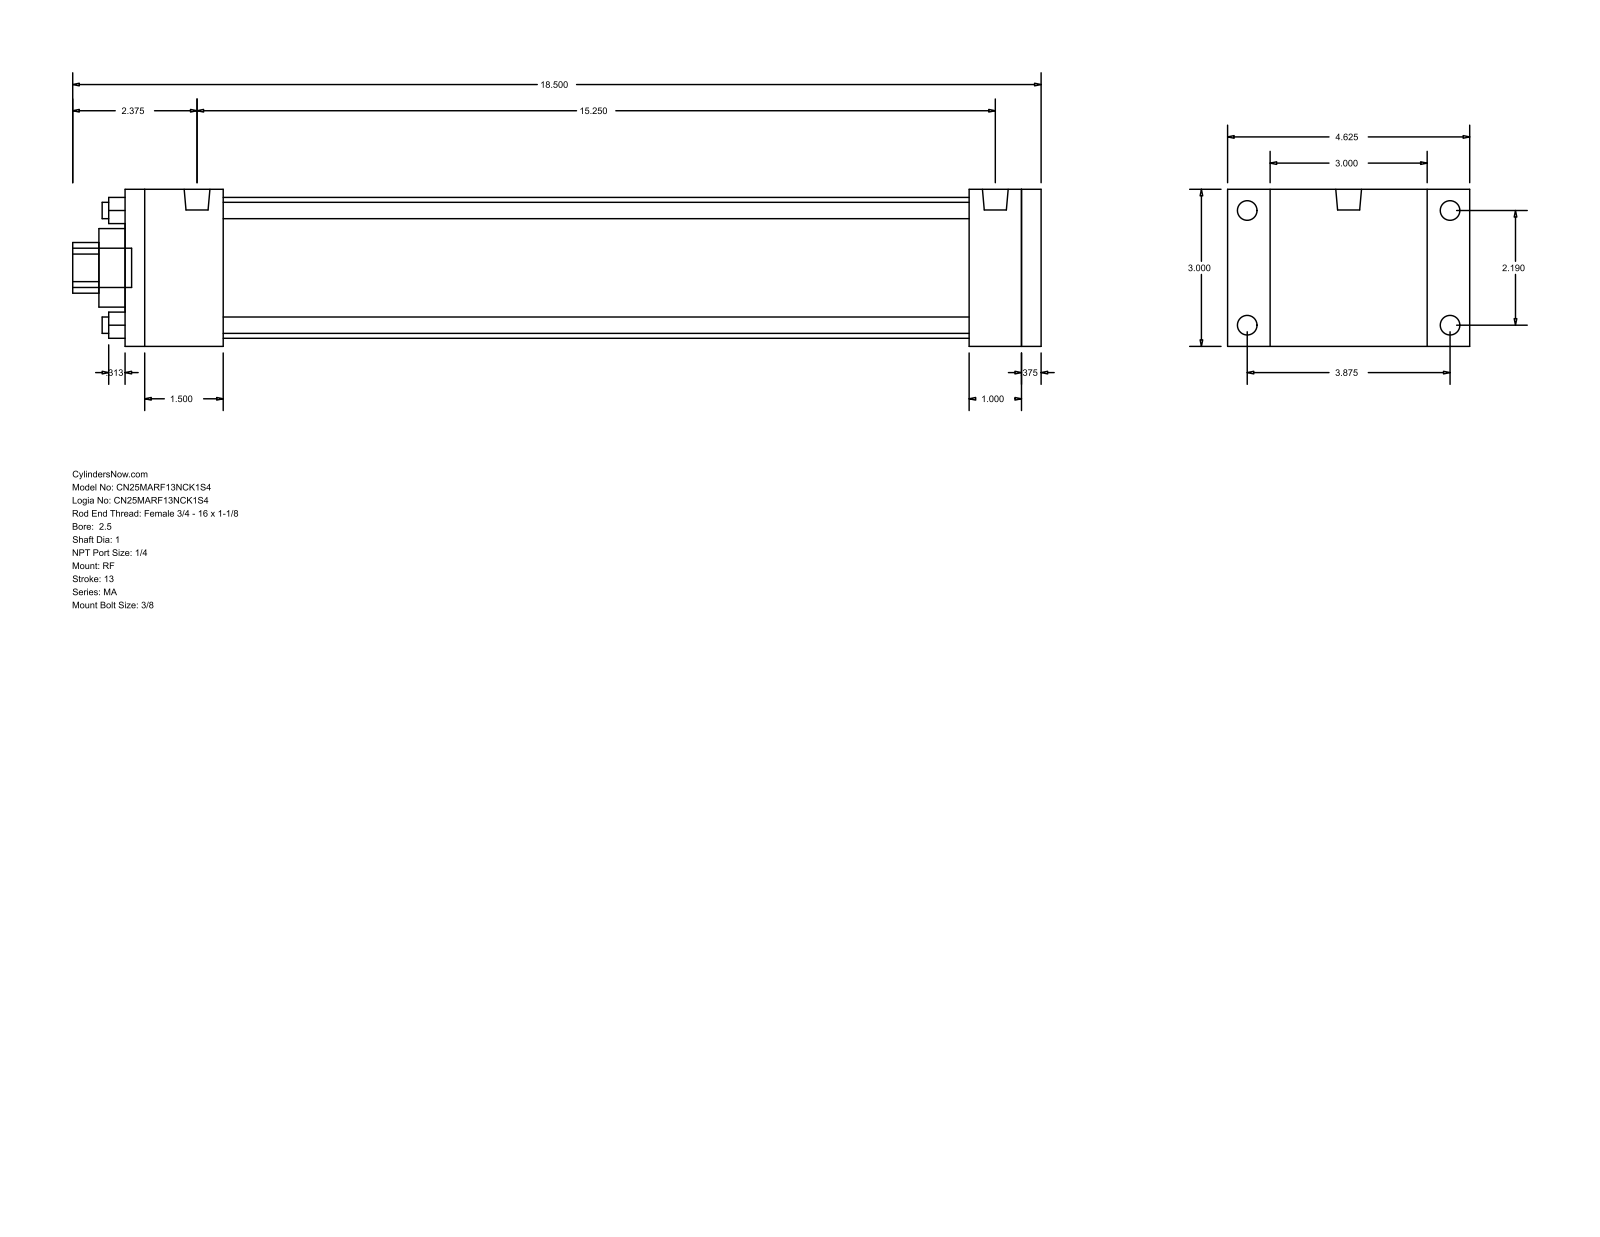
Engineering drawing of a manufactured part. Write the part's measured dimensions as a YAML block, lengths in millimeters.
part_name: "MA_RF__0250_1"
step_written_by: "GSSL Pune (CONFIG_CONTROL_DESIGN)"
units: millimeters
bodies: {solids: 0, faces: 92, planar: 64, cylindrical: 28, other: 0}
overall_size: [469.9, 117.47, 76.2]
round_holes:
  - {diameter: 7.94, count: 4}
  - {diameter: 25.4, count: 1}
  - {diameter: 38.1, count: 1}
  - {diameter: 68.33, count: 1}
round_bosses_or_shafts:
  - {diameter: 9.53, count: 4}
  - {diameter: 7.94, count: 4}
  - {diameter: 12.49, count: 2}
  - {diameter: 19.05, count: 1}
partial_cylinders:
  - {radius: 12.29, count: 1}
face_to_face_distances: [76.2, 444.5, 434.98, 9.52, 25.4, 47.63, 409.58, 361.95, 387.35, 396.87]
hole_center_spacings: [39.33, 55.62, 78.66]
